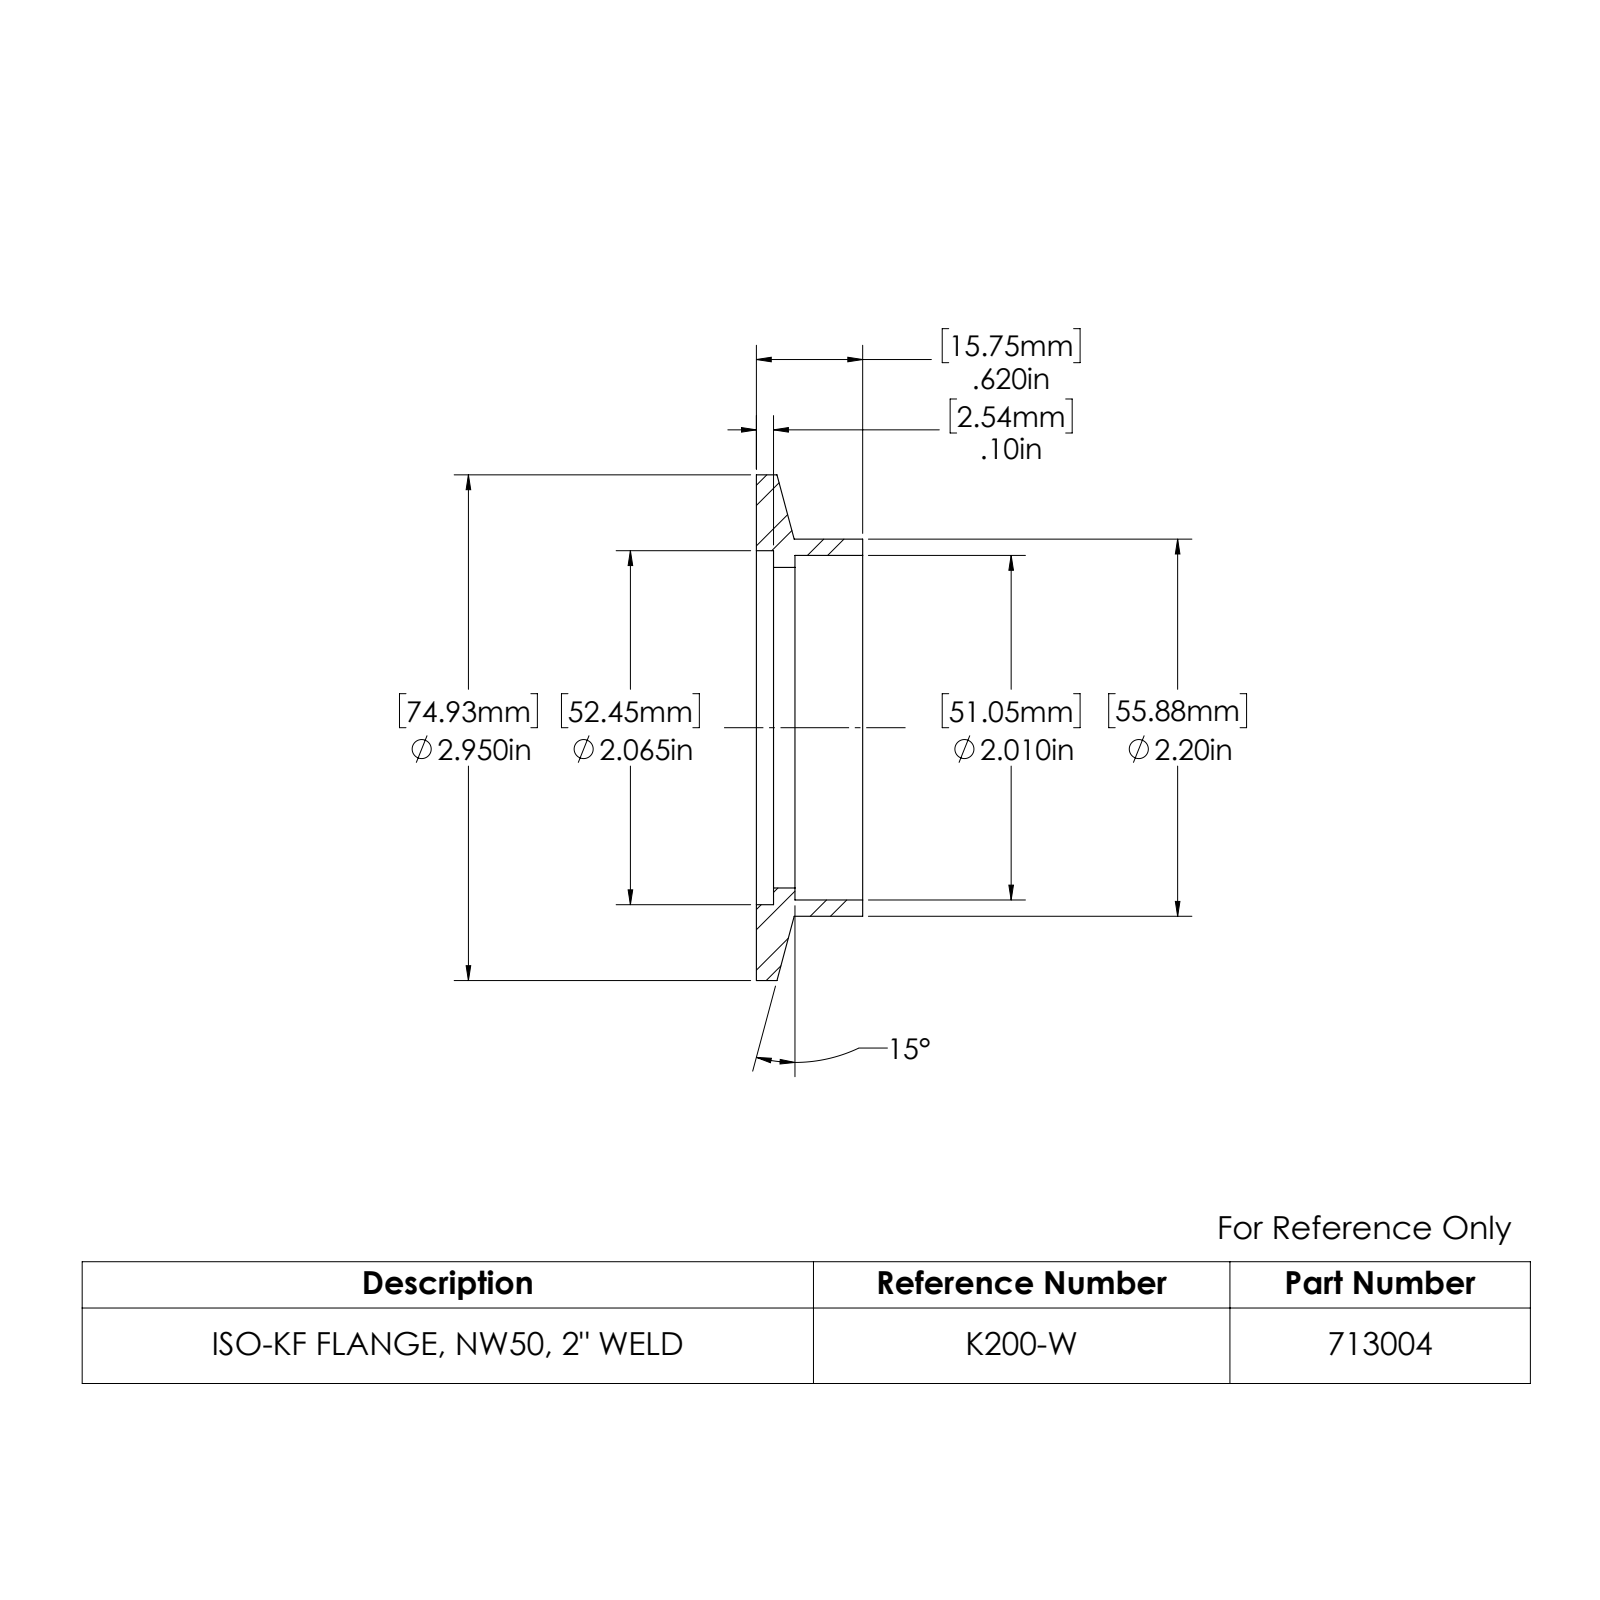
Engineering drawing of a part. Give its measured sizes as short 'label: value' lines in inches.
name: 713004
written by: SolidWorks 2022 (AUTOMOTIVE_DESIGN)
unit: in
bodies: 1 solid, 16 faces (4 planar, 10 cylindrical, 2 other)
size: 2.95 × 2.95 × 0.62
volume: 0.934 in³; area: 16.03 in²
holes: 1× ⌀1.87, 1× ⌀2.01, 1× ⌀2.065
bosses: 1× ⌀2.95, 1× ⌀2.2
face distances: 0.62, 0.52, 0.1, 0.395, 0.125, 0.225
